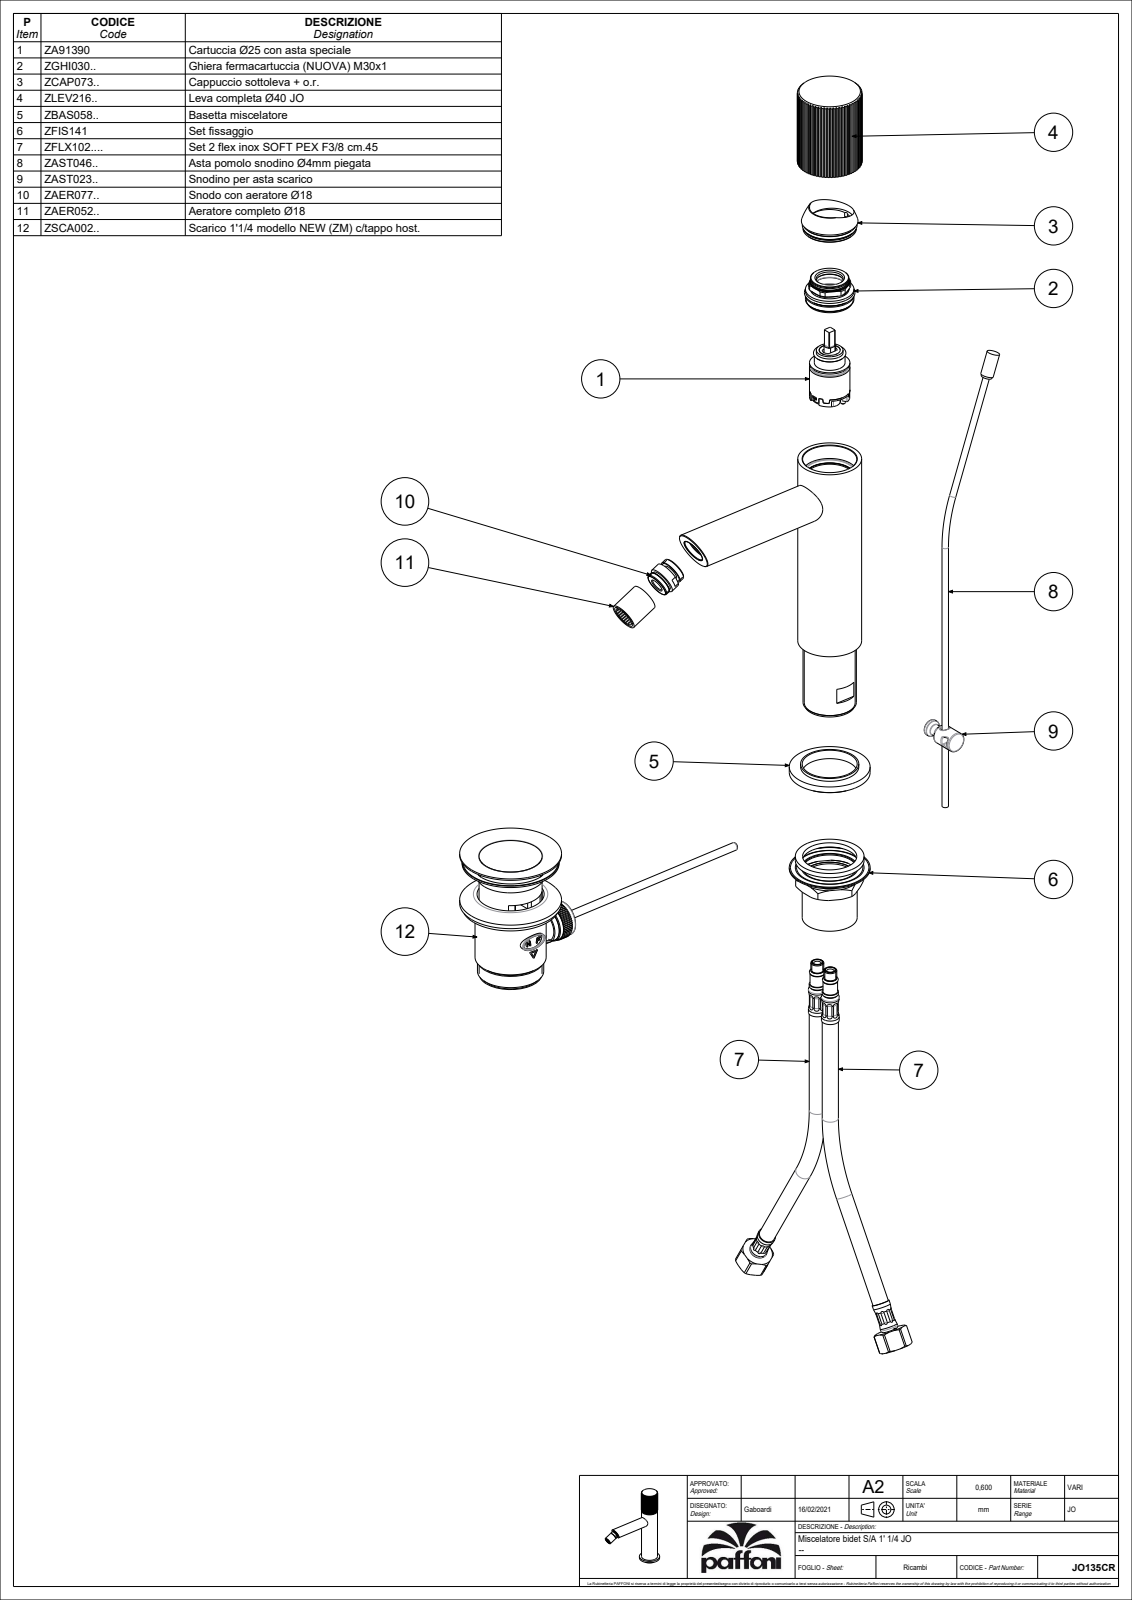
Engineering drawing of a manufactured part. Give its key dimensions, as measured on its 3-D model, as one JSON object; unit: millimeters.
{"part_name": "JO135CR", "step_written_by": "CREO PARAMETRIC BY PTC INC, 2020044 (CONFIG_CONTROL_DESIGN)", "units": "millimeters", "bodies": {"solids": 1, "faces": 238, "planar": 142, "cylindrical": 86, "other": 10}, "overall_size": [186.85, 173.84, 50], "volume_mm3": 280345, "surface_area_mm2": 38706, "round_holes": [[8, 1]], "round_bosses_or_shafts": [[50, 1], [39.5, 1], [24, 1], [18, 1], [14.5, 1], [10, 1], [8, 1], [7.6, 1]], "partial_cylinders_radius": [[20, 1]], "face_to_face_distances": [27.58, 27.59, 4, 27.6, 136.5, 132.5, 2.5, 27.56, 134, 130]}
